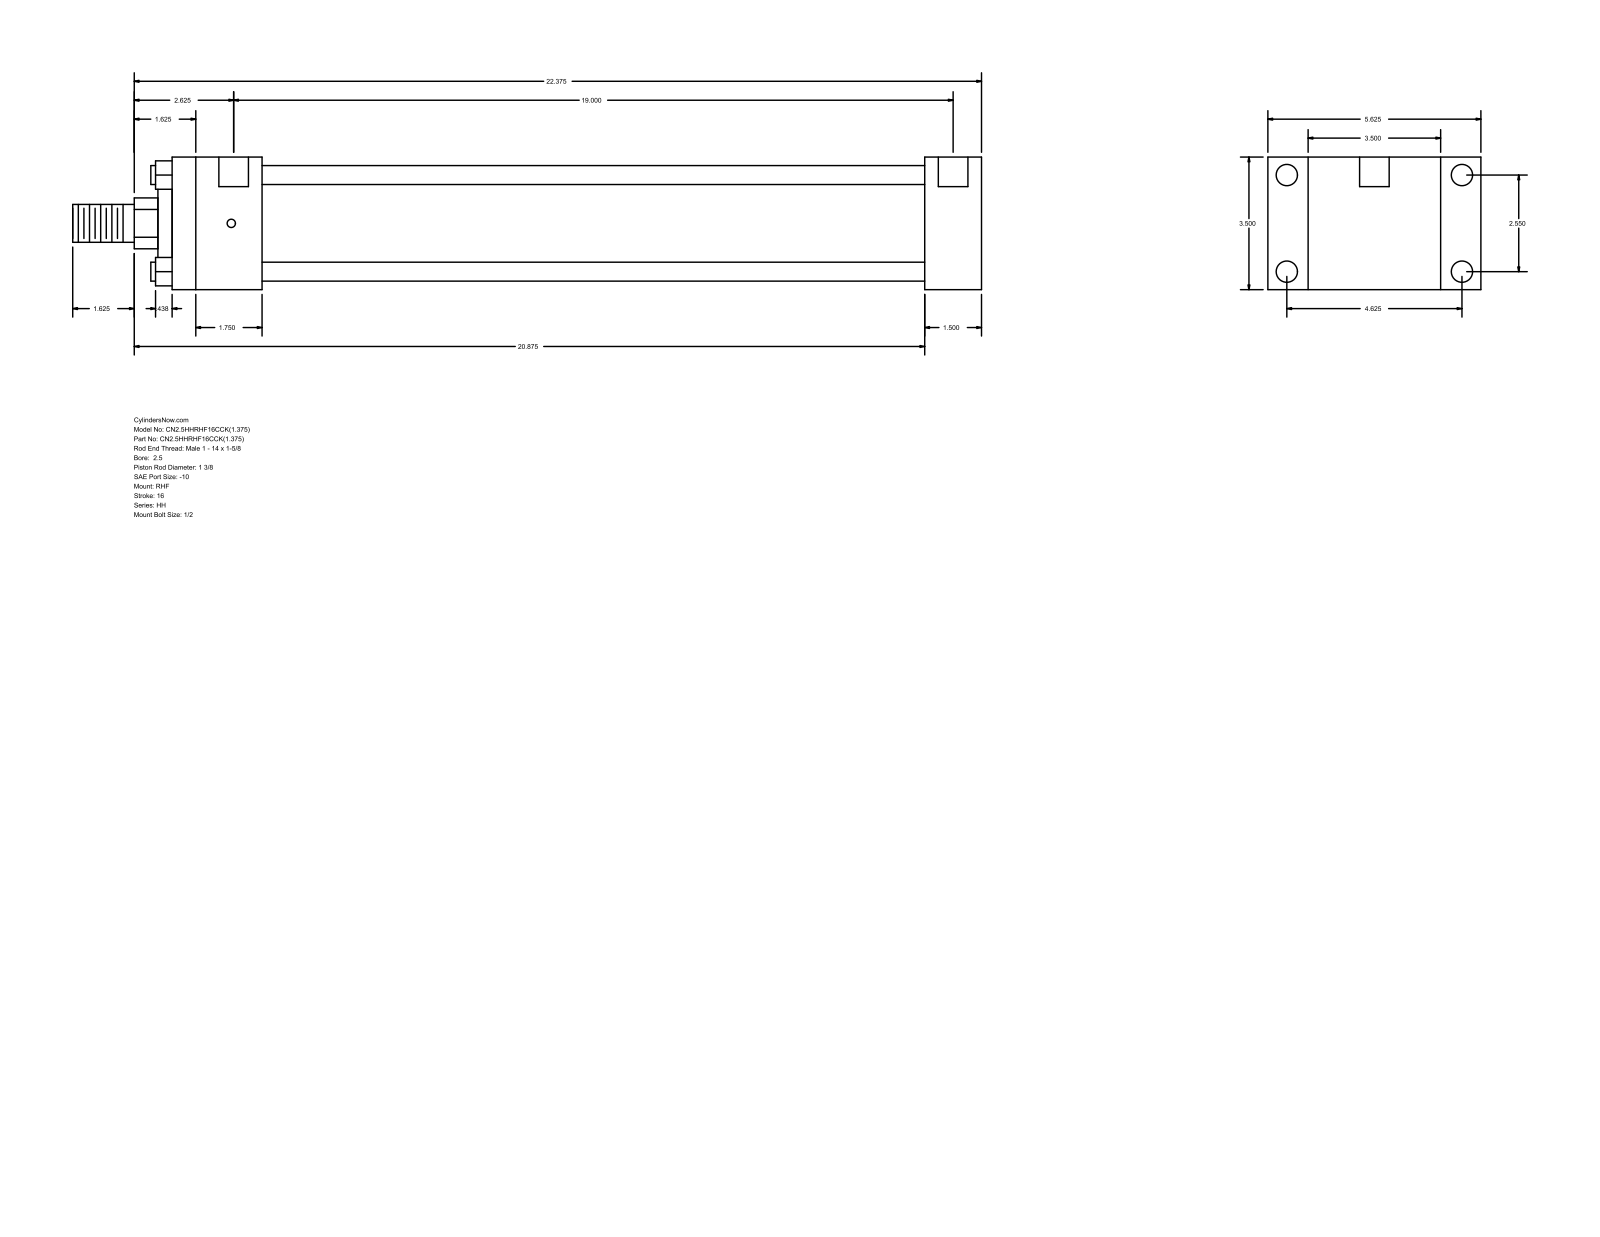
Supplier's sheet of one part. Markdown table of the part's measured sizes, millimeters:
| quantity | value |
| --- | --- |
| part name | HH_RHF__0250_1.375 |
| STEP written by | GSSL Pune (CONFIG_CONTROL_DESIGN) |
| units | millimeters |
| bodies | 0 solids, 88 faces (60 planar, 28 cylindrical, 0 other) |
| overall size | 609.6 × 142.88 × 88.9 |
| round holes (diameter × count) | 5.56 × 4, 14.3 × 4, 19.84 × 2 |
| round bosses / shafts (diameter × count) | 12.7 × 4, 73.03 × 1, 50.8 × 1, 34.92 × 1, 25.4 × 1 |
| partial cylindrical surfaces (radius × count) | 17.06 × 1 |
| main face-to-face distances | 88.9, 38.1, 26.99, 115.89, 504.83, 542.93, 142.88, 60.32, 444.51, 482.61 |
| hole center spacings | 64.76, 117.48, 134.15, 485.77, 1.58, 1.59, 482.6, 484.18 |
